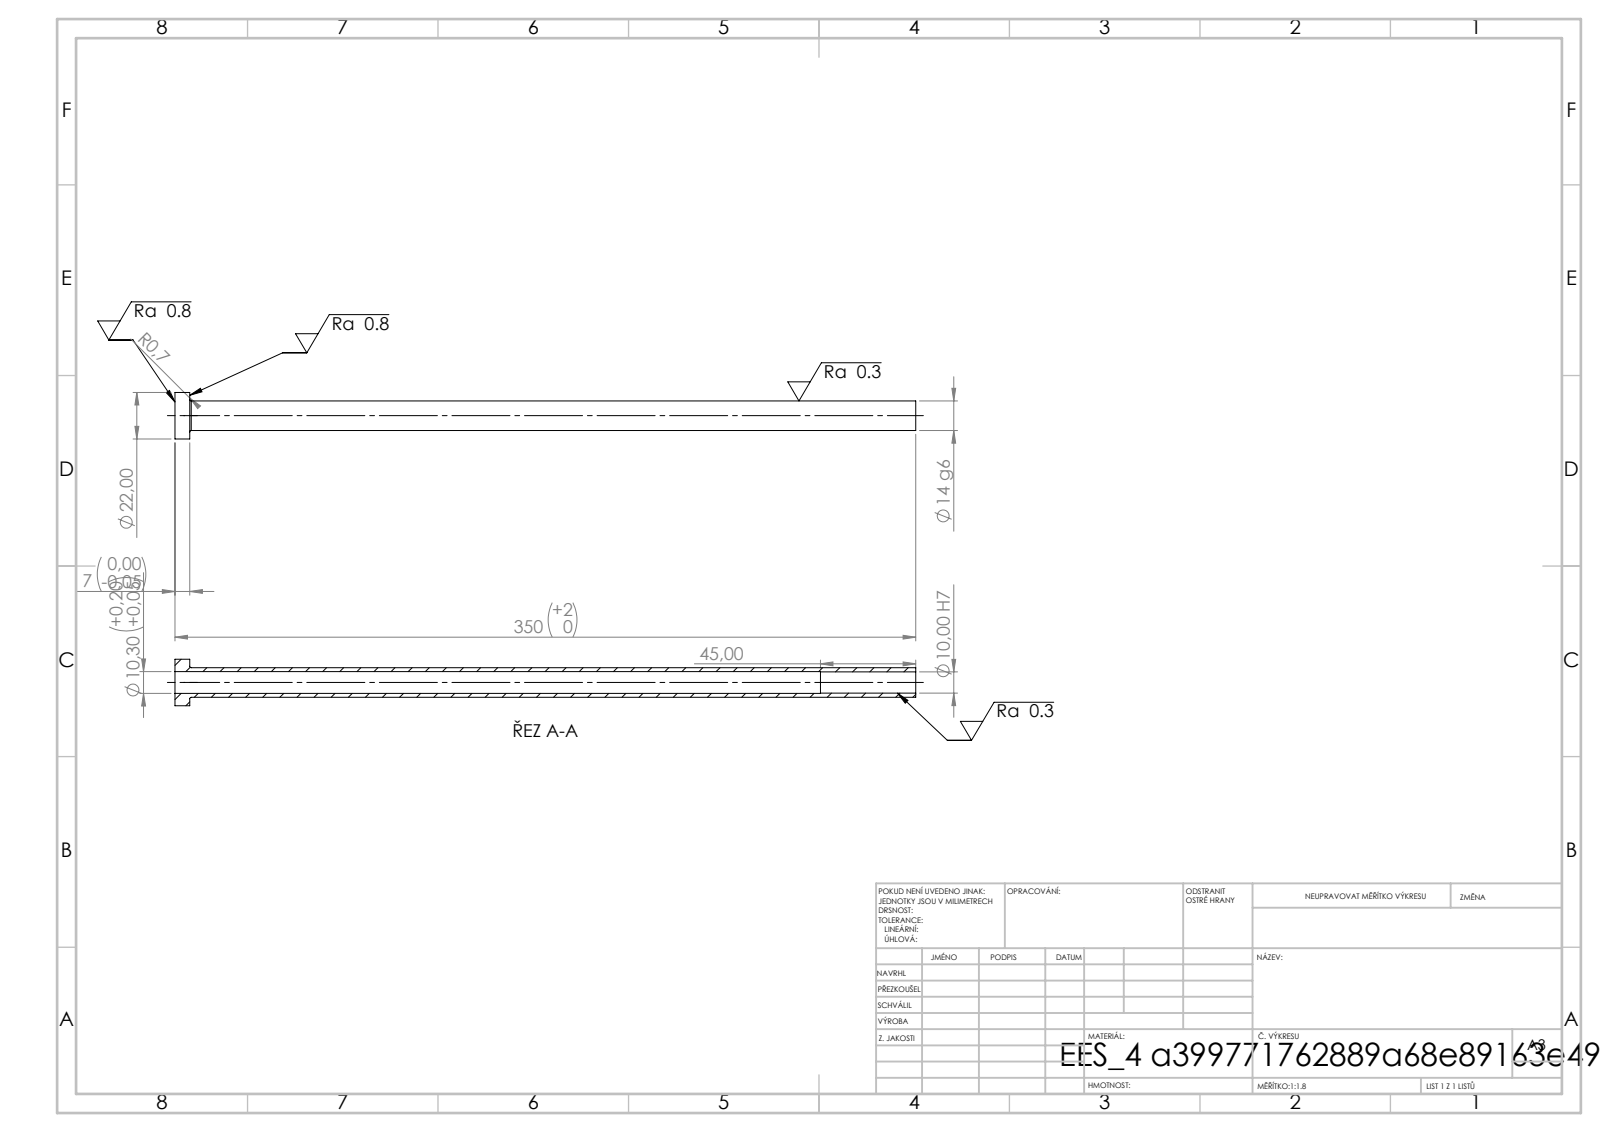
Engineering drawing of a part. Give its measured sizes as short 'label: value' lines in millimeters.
written by: SolidWorks 2019 (CONFIG_CONTROL_DESIGN)
unit: mm
bodies: 1 solid, 14 faces (4 planar, 8 cylindrical, 2 other)
size: 350 × 22 × 22
volume: 26 519 mm³; area: 27 443 mm²
holes: 1× ⌀10, 1× ⌀10.3
bosses: 1× ⌀22, 1× ⌀14
face distances: 7, 350, 343, 305, 298, 45
